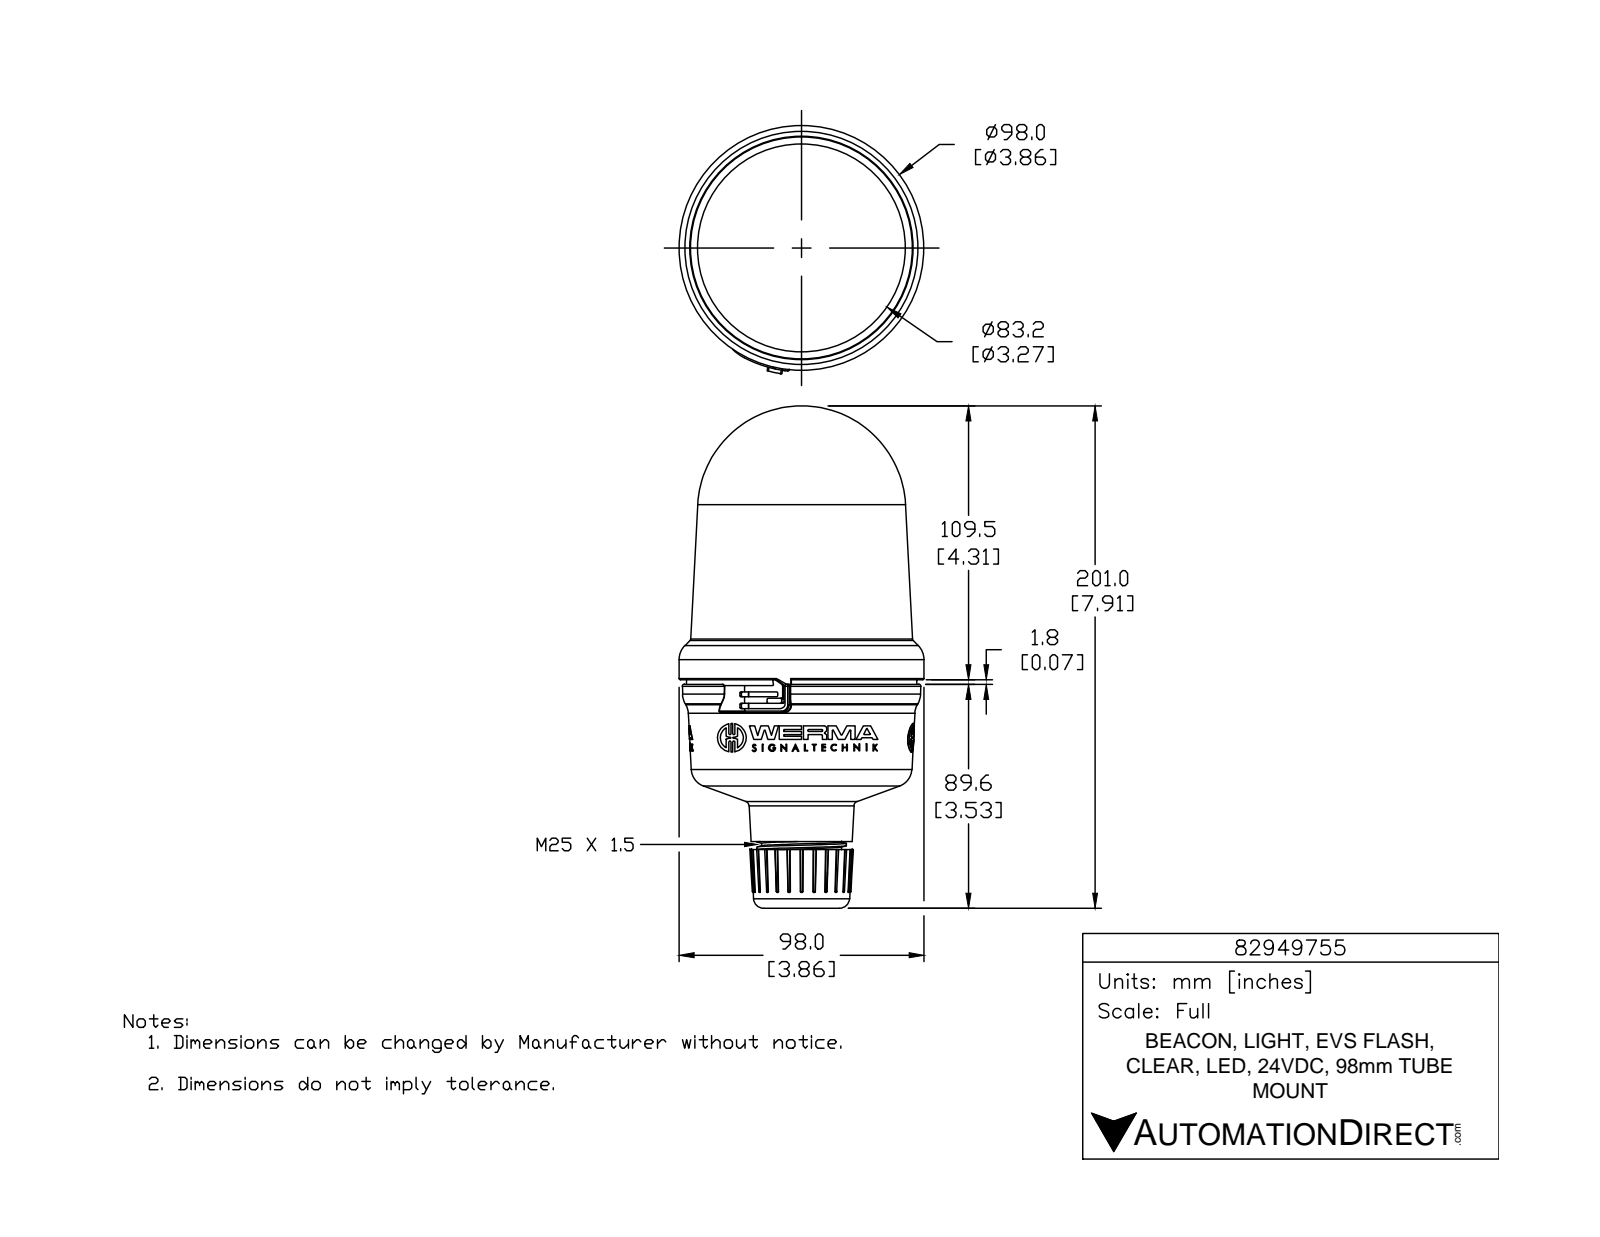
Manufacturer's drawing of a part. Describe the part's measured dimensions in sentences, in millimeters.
The part is named "82949755". Its 3-D file was written by "SolidWorks 2015 (AUTOMOTIVE_DESIGN)". It is 1 solid with 1006 faces: 554 planar, 189 cylindrical and 263 other. Overall it measures 201 by 99.4 by 98 millimeters. Its volume is 896 400 cubic millimeters and its surface area 58 960 square millimeters. Round holes: 3 of diameter 2, 1 of diameter 25.7, 1 of diameter 26. Round bosses or shafts: 3 of diameter 11.5, 3 of diameter 2.9, 1 of diameter 98, 1 of diameter 35.8, 1 of diameter 32. Partial cylindrical surfaces (rounded edges, fillets, slot ends): 12 of radius 0.5, 9 of radius 0.2, 6 of radius 0.2, 6 of radius 0.4, 6 of radius 0.4, 6 of radius 0.4, 6 of radius 6.7, 3 of radius 0.2. The main face-to-face distances are 56.2, 11.7, 68, 8.5, 3.2, 64.7, 66.1, 62.9, 54.4, 1.9.
